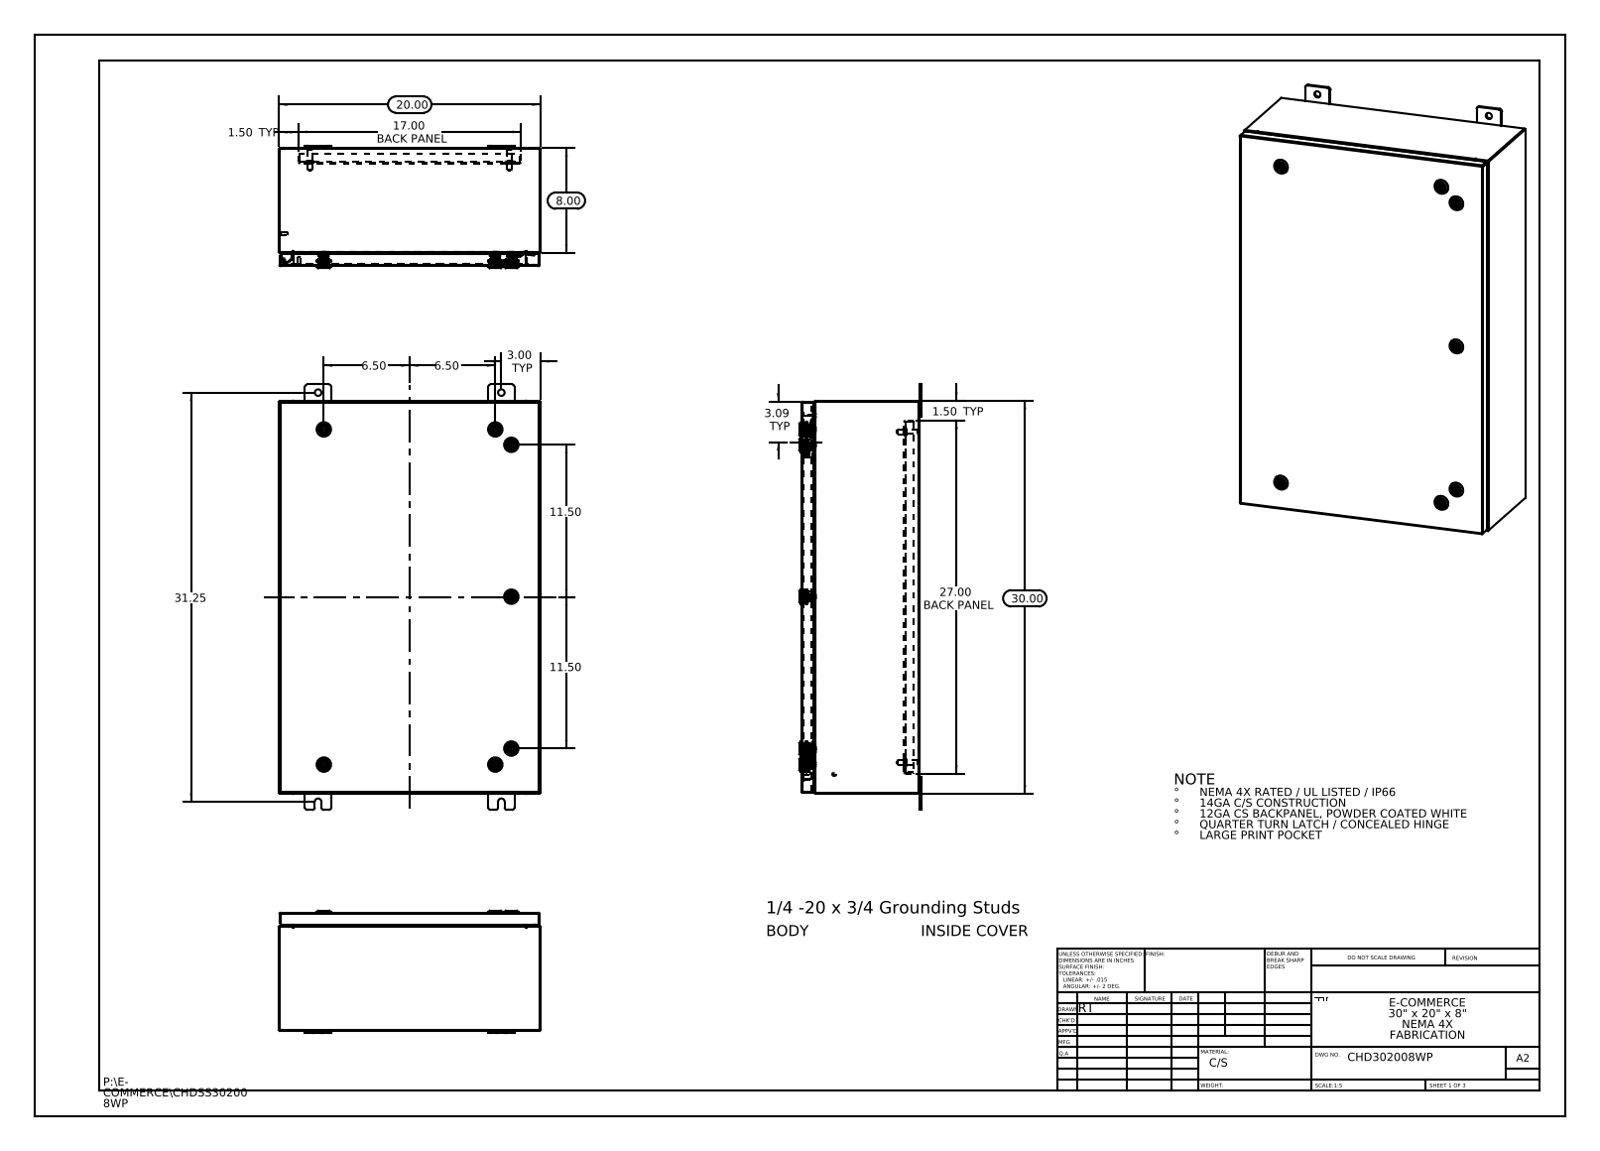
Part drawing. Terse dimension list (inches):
name: CHDSS302008WP Mounting Feet; Washer-221320-IB-Industrilas_Washer-221320-IB-Industrilas; Concealed Hinge enclosure side; Concealed Hinge (Cover Side) (+8 more)
written by: SolidWorks 2013 (CONFIG_CONTROL_DESIGN)
unit: in
bodies: 60 solids, 6230 faces (1808 planar, 1940 cylindrical, 2482 other)
size: 32.5 × 20 × 9.356
volume: 230.8 in³; area: 5 739 in²
holes: 8× ⌀0.5, 7× ⌀0.197, 7× ⌀0.394, 7× ⌀0.4, 7× ⌀0.63, 7× ⌀0.787, 4× ⌀0.136, 1× ⌀0.211
bosses: 9× ⌀0.236, 7× ⌀1.102, 7× ⌀0.78, 7× ⌀0.626, 7× ⌀0.61, 7× ⌀0.531, 7× ⌀0.392, 7× ⌀0.114
rounds: 231× R0.006, 231× R0.118, 84× R0.028, 28× R0.02, 28× R0.197, 24× R0.19, 22× R0.013, 18× R0.088
face distances: 0.075, 0.074, 9.01, 8.935, 8.936, 8.861, 0.104, 19.925, 1, 1.075
hole spacings: 1.858, 3.065, 11.6, 13.1, 14, 15.25, 25.25, 25.6
